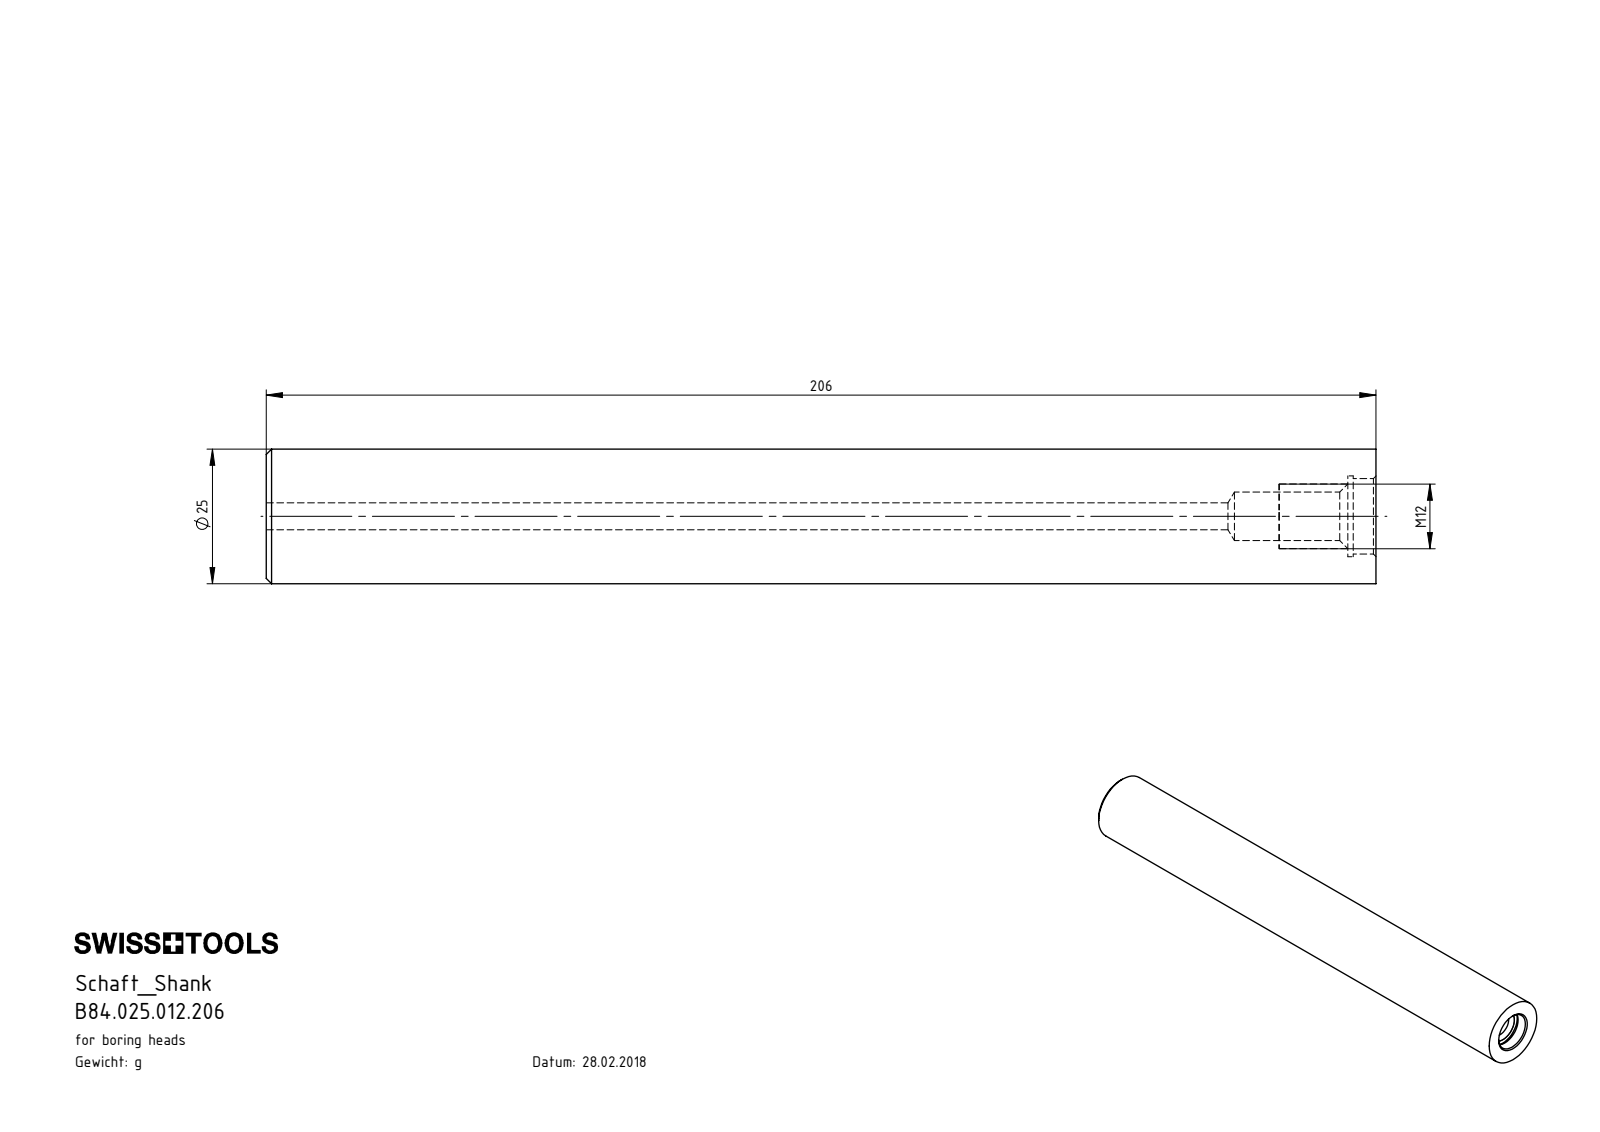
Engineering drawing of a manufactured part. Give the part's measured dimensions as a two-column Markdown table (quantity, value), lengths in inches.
| quantity | value |
| --- | --- |
| part name | B84.025.012.206 |
| STEP written by | SolidWorks 2017 (CONFIG_CONTROL_DESIGN) |
| units | inches |
| bodies | 1 solid, 22 faces (4 planar, 10 cylindrical, 8 other) |
| overall size | 8.11 × 0.984 × 0.984 |
| volume | 5.817 in³ |
| surface area | 32.13 in² |
| round holes (diameter × count) | 0.197 × 1, 0.354 × 1, 0.551 × 1, 0.591 × 1 |
| round bosses / shafts (diameter × count) | 0.984 × 1 |
| main face-to-face distances | 8.11, 7.904, 0.207, 7.943, 0.039, 0.167 |
